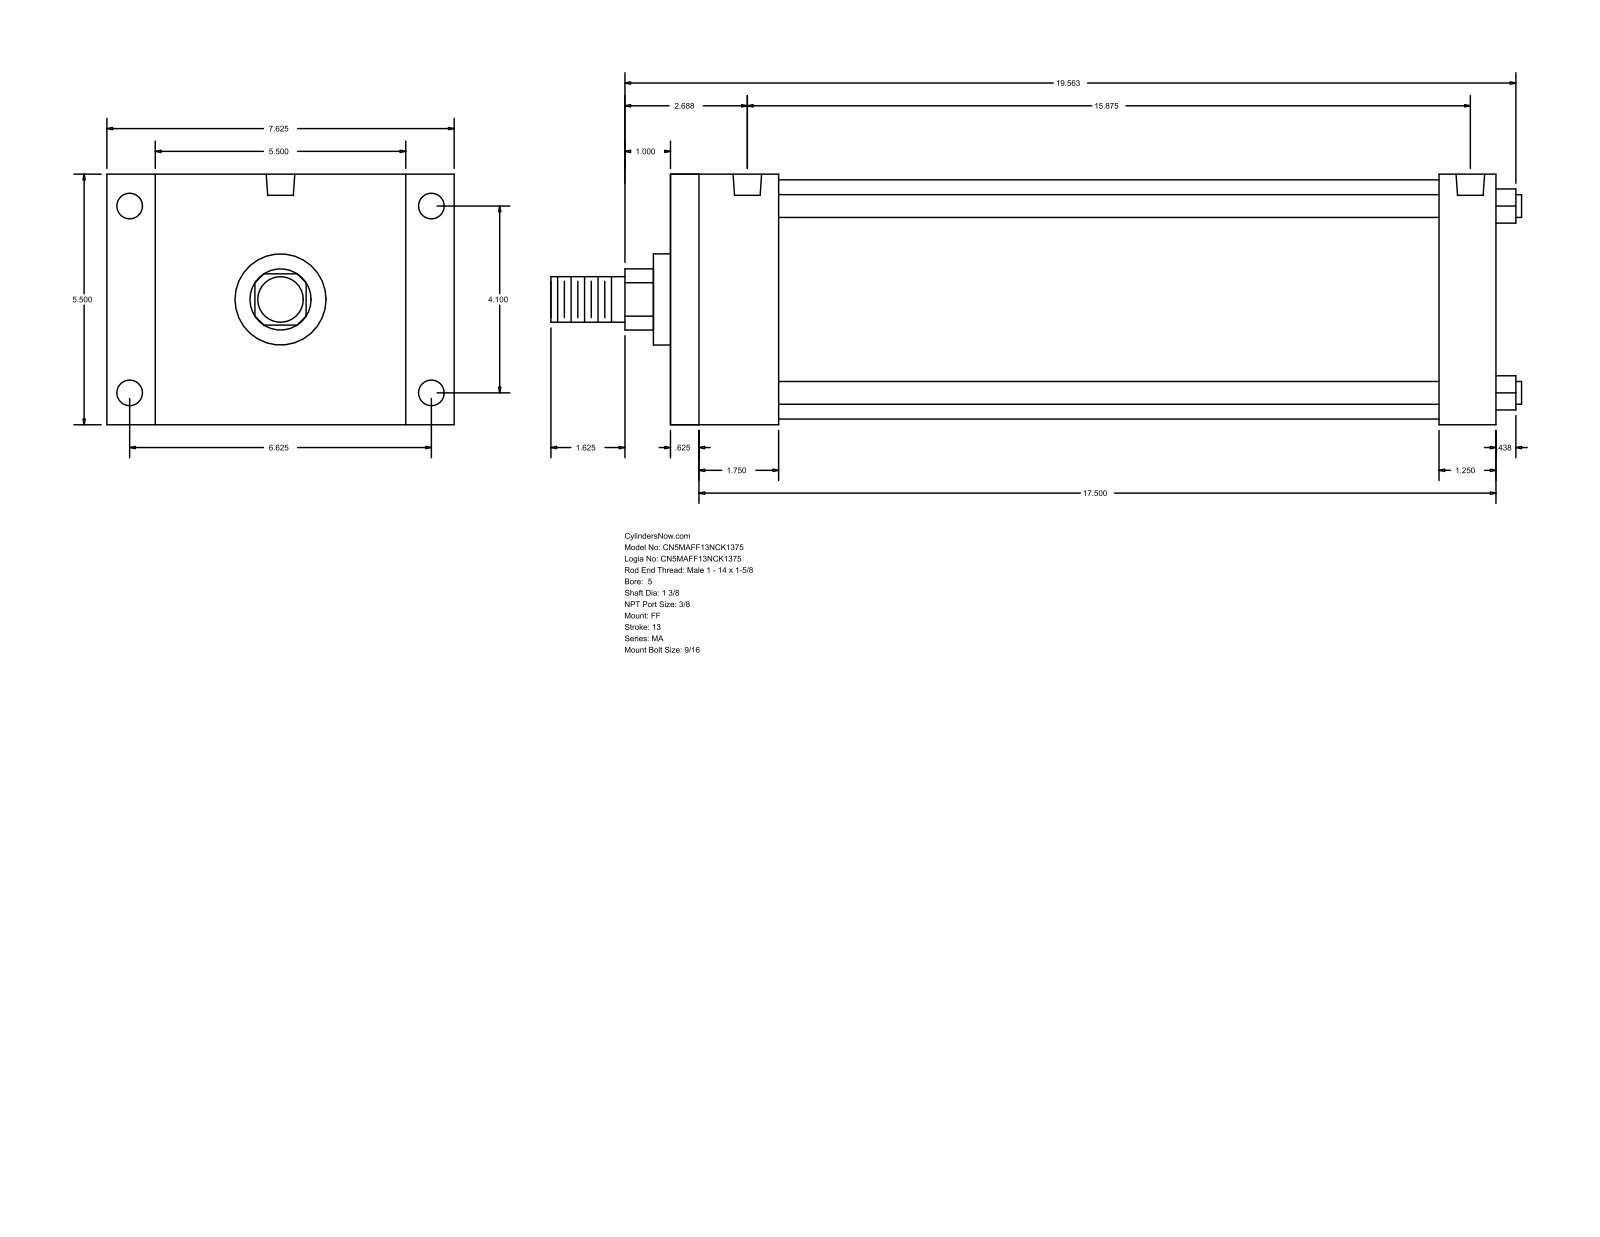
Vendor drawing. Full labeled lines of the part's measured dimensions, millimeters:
Part name (STEP PRODUCT): MA_FF__0500_1.375
STEP written by: GSSL Pune (CONFIG_CONTROL_DESIGN)
Units: millimetres
Bodies: 0 solids, 92 faces (64 planar, 28 cylindrical, 0 other)
Overall size (bounding box): 541.34 × 193.68 × 139.7
Round holes (diameter × count): ⌀11.11 ×4, ⌀14.29 ×4, ⌀15.93 ×2
Round bosses / shafts (diameter × count): ⌀12.7 ×4, ⌀133.35 ×1, ⌀50.8 ×1, ⌀34.92 ×1, ⌀25.4 ×1
Partial cylindrical surfaces — rounded edges, fillets, slot ends (radius × count): R17.06 ×1
Main face-to-face distances: 139.7, 460.37, 15.87, 444.5, 428.62, 412.75, 31.75, 60.32, 44.45, 368.3
Hole centre spacings: 104.14, 168.28, 197.9, 393.7, 4.76, 4.77, 398.46, 398.47
